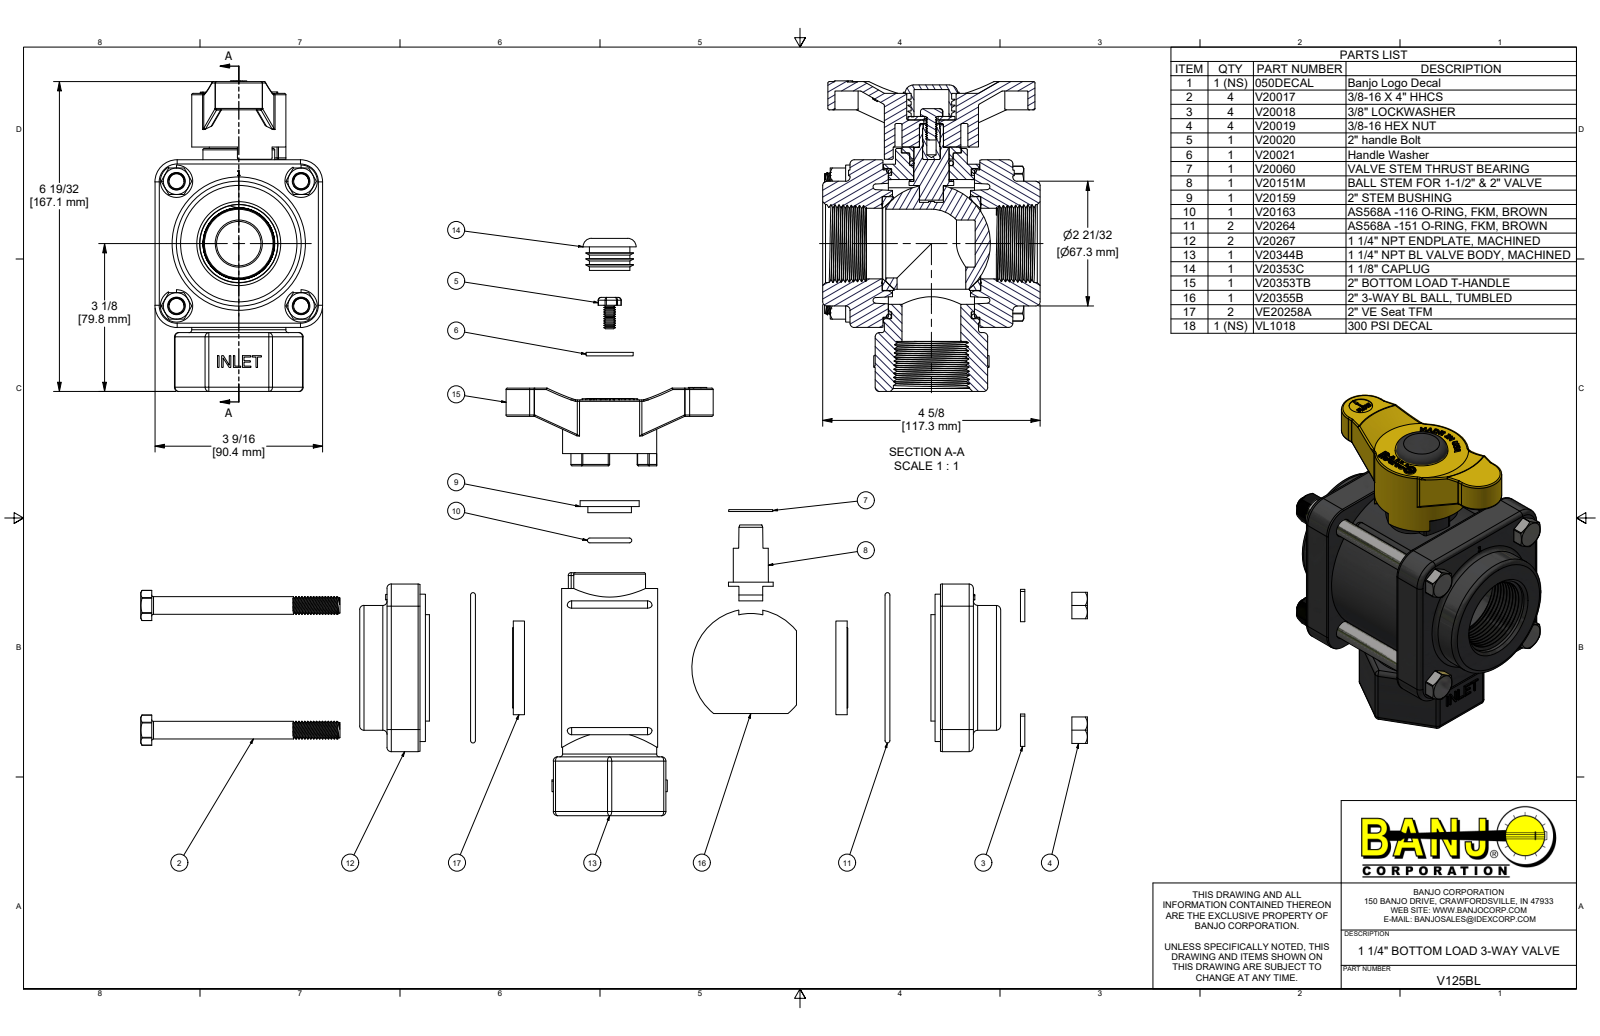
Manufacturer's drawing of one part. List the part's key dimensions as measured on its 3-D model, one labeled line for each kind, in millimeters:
Part name (STEP PRODUCT): V125BL; V20021; V20344B; V20344BX (+8 more)
STEP written by: Autodesk Inventor 2022 (AUTOMOTIVE_DESIGN)
Units: millimetres
Bodies: 30 solids, 2964 faces (1364 planar, 560 cylindrical, 1040 other)
Overall size (bounding box): 167.5 × 117.3 × 90.4
Volume: 681 700 mm³ · Surface area: 202 600 mm²
Round holes (diameter × count): ⌀7.8 ×4, ⌀9.8 ×4, ⌀10.3 ×4, ⌀37.1 ×2, ⌀4.4 ×1, ⌀5 ×1, ⌀5.8 ×1, ⌀6.2 ×1, ⌀7.1 ×1, ⌀8.1 ×1, ⌀8.2 ×1, ⌀8.9 ×1
Round bosses / shafts (diameter × count): ⌀8.2 ×60, ⌀17.4 ×4, ⌀9.5 ×4, ⌀85.6 ×1, ⌀79.5 ×1, ⌀73.7 ×1, ⌀67.3 ×1, ⌀57.4 ×1
Partial cylindrical surfaces — rounded edges, fillets, slot ends (radius × count): R0.8 ×70, R2.3 ×34, R1.5 ×10, R1.9 ×8, R4.1 ×8, R1.6 ×4, R2.4 ×4, R3.2 ×4
Main face-to-face distances: 17.8, 20.7, 70.1, 67.2, 2.9, 49.4, 90.4, 87.9, 32.5, 17.3
Hole centre spacings: 47.5, 67.3, 95.1, 19.9, 46.4, 58
